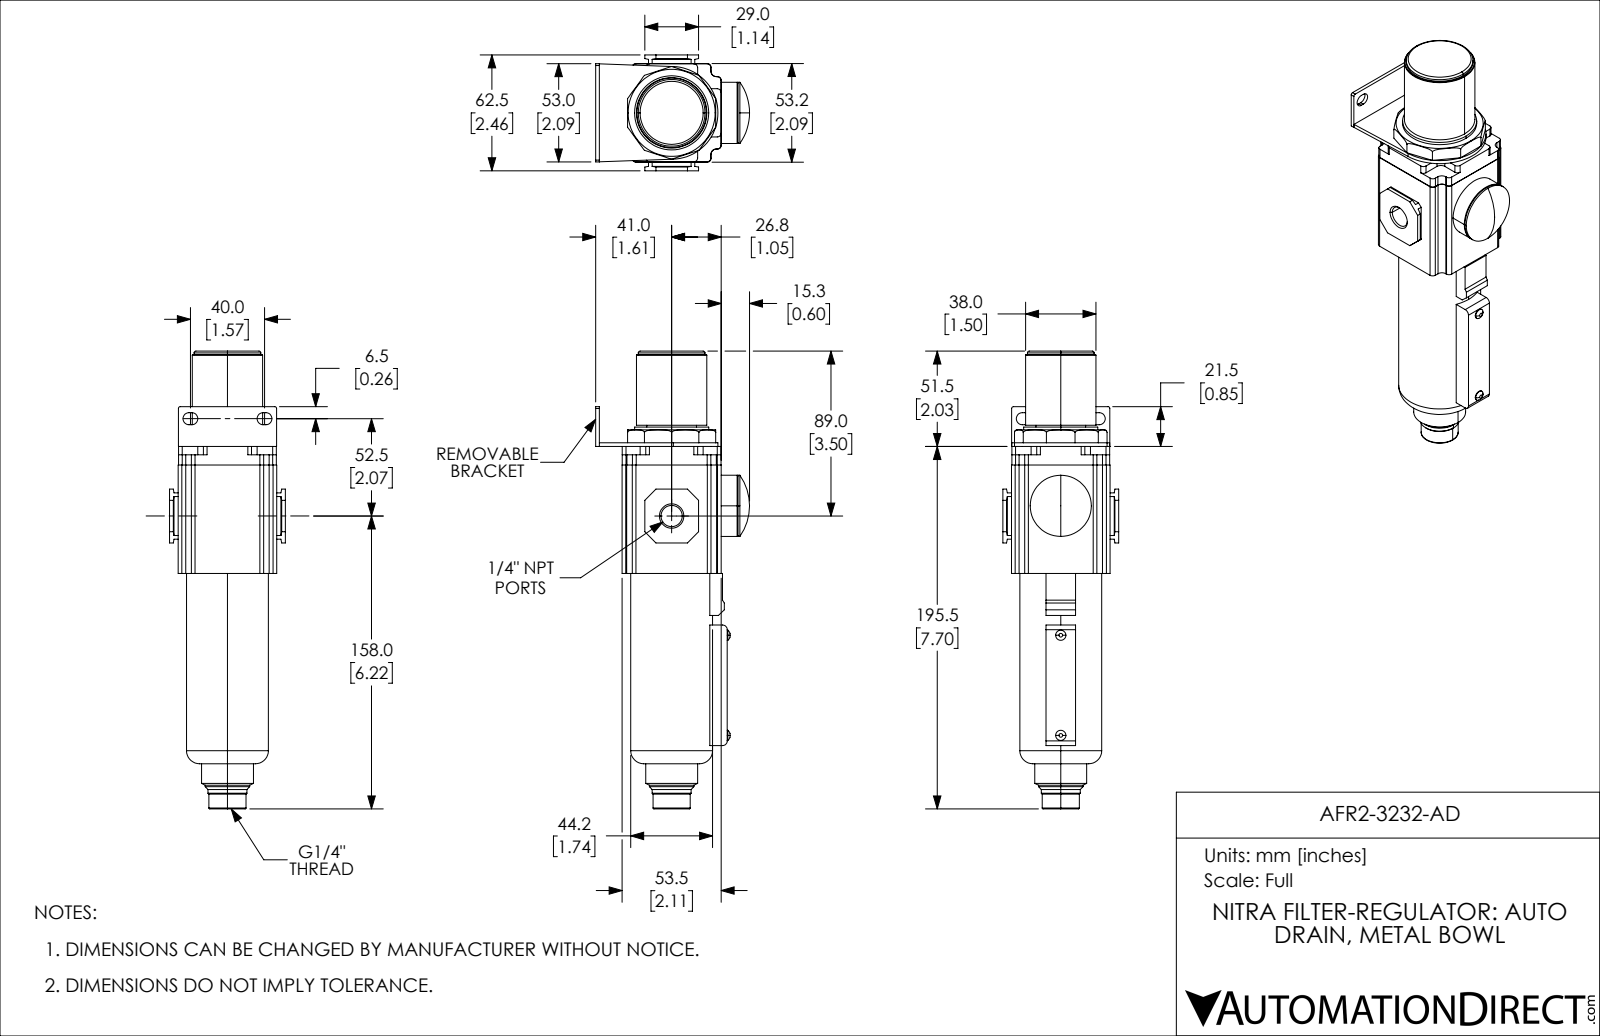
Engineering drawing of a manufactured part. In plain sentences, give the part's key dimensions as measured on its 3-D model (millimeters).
The part is named "AFR2-3232-AD". Its 3-D file was written by "SolidWorks 2019 (CONFIG_CONTROL_DESIGN)". It is 1 solid with 235 faces: 128 planar, 77 cylindrical and 30 other. Overall it measures 247 by 83.03 by 62.5 millimeters. Its volume is 442 048 cubic millimeters and its surface area 52 289 square millimeters. Round holes: 2 of diameter 11.45. Round bosses or shafts: 2 of diameter 5.5, 1 of diameter 44.2, 1 of diameter 40, 1 of diameter 38, 1 of diameter 36, 1 of diameter 33, 1 of diameter 28, 1 of diameter 26.78. Partial cylindrical surfaces (rounded edges, fillets, slot ends): 24 of radius 2, 12 of radius 3, 4 of radius 3.25, 2 of radius 1, 2 of radius 2.5, 1 of radius 25. The main face-to-face distances are 2, 53.2, 18.6, 34.6, 39.25, 16, 53.5, 4.65, 23.25, 57.85.
